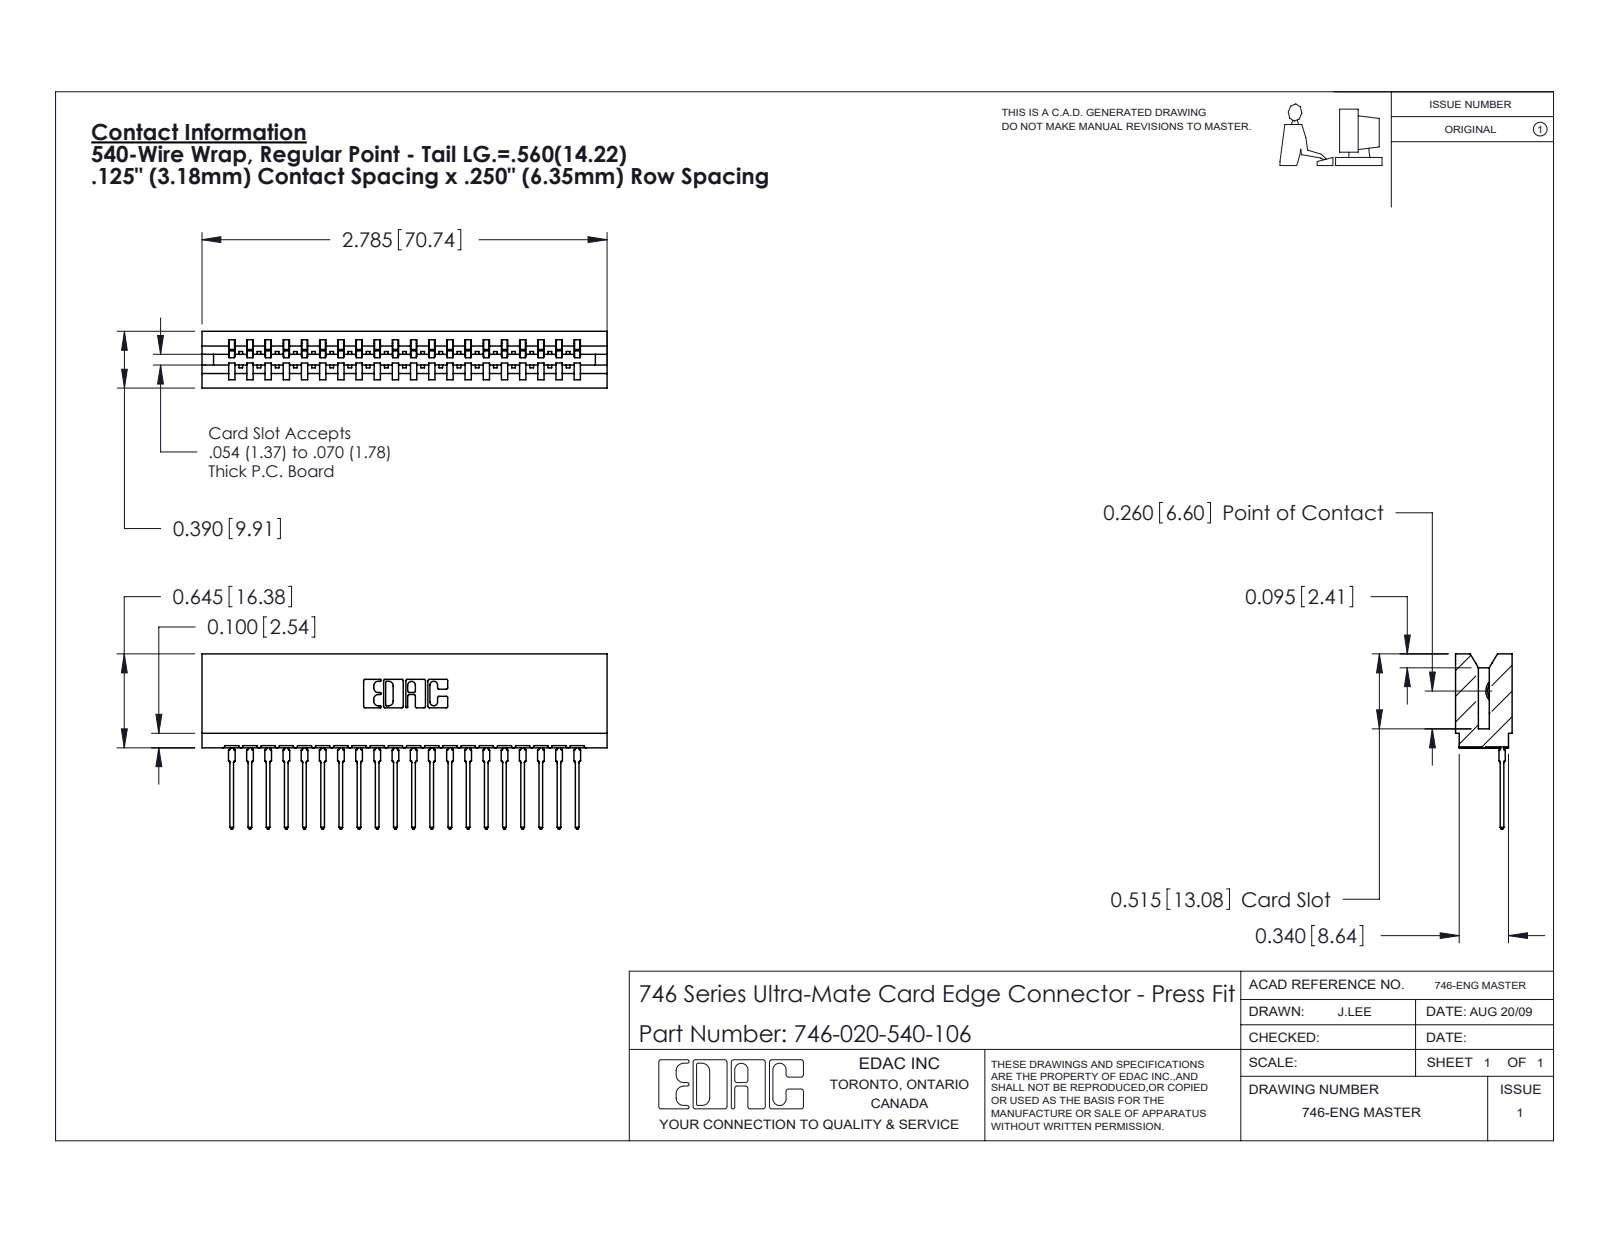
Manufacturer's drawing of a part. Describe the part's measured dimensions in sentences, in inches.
The part is named "746 Part_.515 Slot Depth - 06; 746-292-001_540; 746-020-540-106". Its 3-D file was written by "SolidWorks 2020 (CONFIG_CONTROL_DESIGN)". It is 21 solids with 2258 faces: 1316 planar, 422 cylindrical and 520 other. Overall it measures 2.785 by 1.204 by 0.39 inches. Its volume is 0.462 cubic inches and its surface area 17.21 square inches. Partial cylindrical surfaces (rounded edges, fillets, slot ends): 40 of radius 0.021, 22 of radius 0.01, 21 of radius 0.015, 6 of radius 0.007, 6 of radius 0.031, 4 of radius 0.005, 4 of radius 0.011, 3 of radius 0.026. The main face-to-face distances are 0.25, 0.333, 0.057, 0.39, 0.5, 0.025, 0.307, 0.083, 0.125, 0.375.
